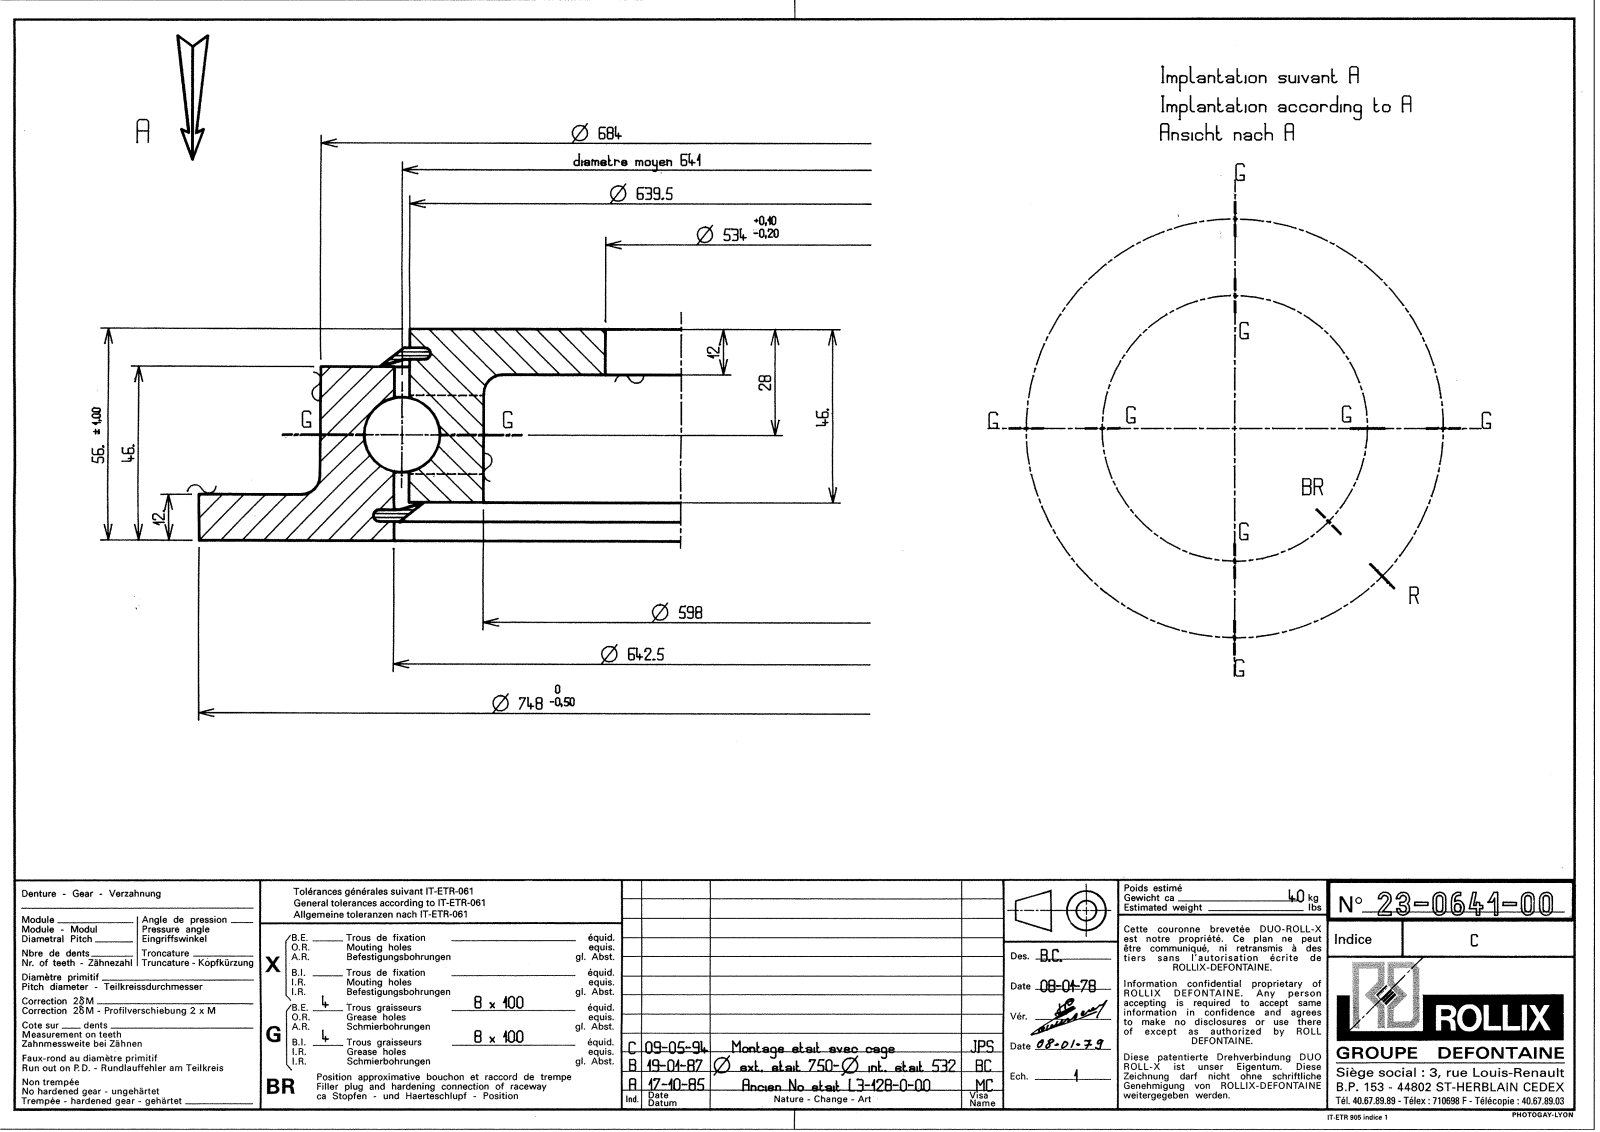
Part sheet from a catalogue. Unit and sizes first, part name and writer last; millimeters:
Units: millimetres
Overall size (bounding box): 748 × 748 × 56
Round holes (diameter × count): ⌀7 ×8, ⌀534 ×1, ⌀598 ×1, ⌀645.5 ×1
Round bosses / shafts (diameter × count): ⌀8 ×8, ⌀748 ×1, ⌀684 ×1, ⌀636.5 ×1
Main face-to-face distances: 12, 44, 56, 10, 46, 2, 34, 32, 36, 4.95
Volume: 4 776 000 mm³ · Surface area: 965 207 mm²
Bodies: 13 solids, 258 faces (94 planar, 52 cylindrical, 112 other)
Part name (STEP PRODUCT): 23-0641-00
STEP written by: SolidWorks 2016 (CONFIG_CONTROL_DESIGN)
